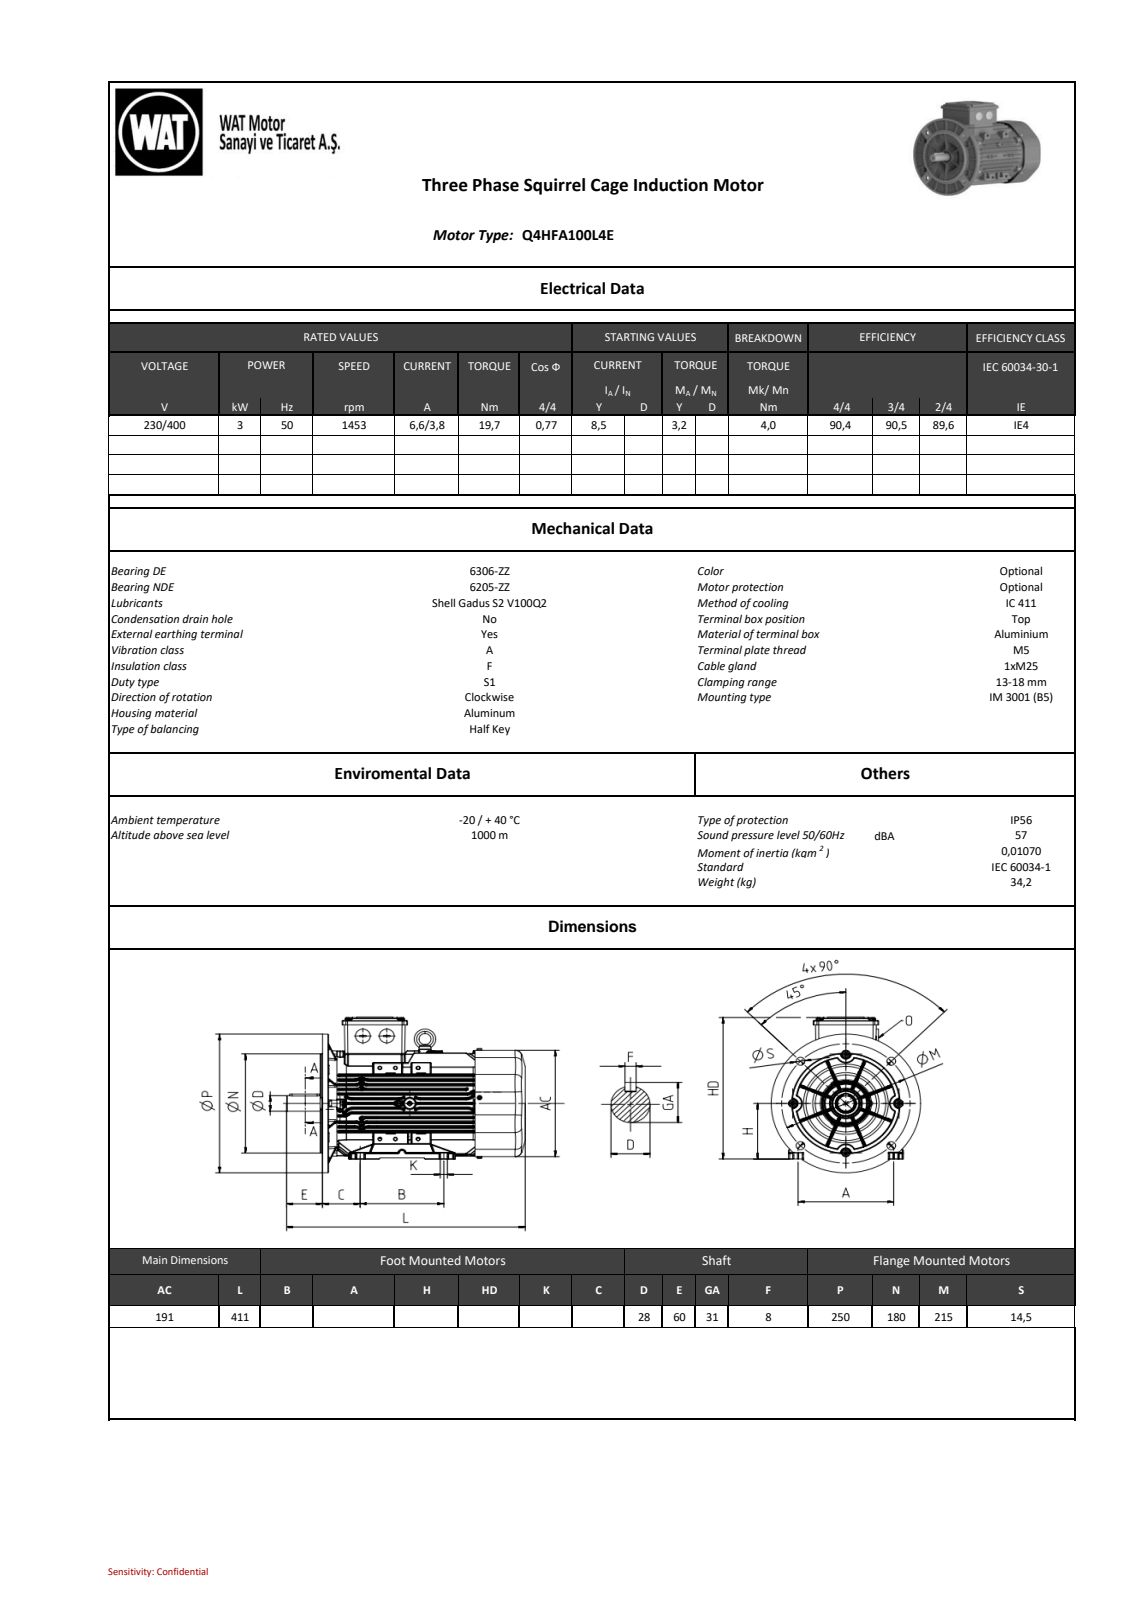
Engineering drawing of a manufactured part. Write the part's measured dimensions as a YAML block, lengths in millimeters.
part_name: "QH100 B35 KTA-M2_stp_objects"
step_written_by: "SIEMENS PLM Software NX2206.8101 (AUTOMOTIVE_DESIGN)"
units: millimeters
bodies: {solids: 0, faces: 5549, planar: 1212, cylindrical: 2112, other: 2225}
overall_size: [411.25, 267.54, 249.94]
round_holes:
  - {diameter: 4, count: 1}
  - {diameter: 10, count: 1}
  - {diameter: 10.5, count: 1}
  - {diameter: 12, count: 1}
  - {diameter: 43.9, count: 1}
  - {diameter: 44.1, count: 1}
  - {diameter: 52, count: 1}
  - {diameter: 57.4, count: 1}
  - {diameter: 78, count: 1}
  - {diameter: 89, count: 1}
  - {diameter: 129, count: 1}
round_bosses_or_shafts:
  - {diameter: 8, count: 8}
  - {diameter: 8.28, count: 4}
  - {diameter: 180.5, count: 1}
  - {diameter: 113.5, count: 1}
  - {diameter: 93.5, count: 1}
  - {diameter: 61, count: 1}
  - {diameter: 30, count: 1}
  - {diameter: 29, count: 1}
partial_cylinders:
  - {radius: 1, count: 635}
  - {radius: 0.8, count: 558}
  - {radius: 2, count: 85}
  - {radius: 0.81, count: 53}
  - {radius: 0.5, count: 37}
  - {radius: 5, count: 36}
  - {radius: 15, count: 26}
  - {radius: 4.5, count: 16}
face_to_face_distances: [8.53, 8.46, 8.45, 76.24, 16.91, 93.45, 25.58, 17.05, 76.68, 59.63]
